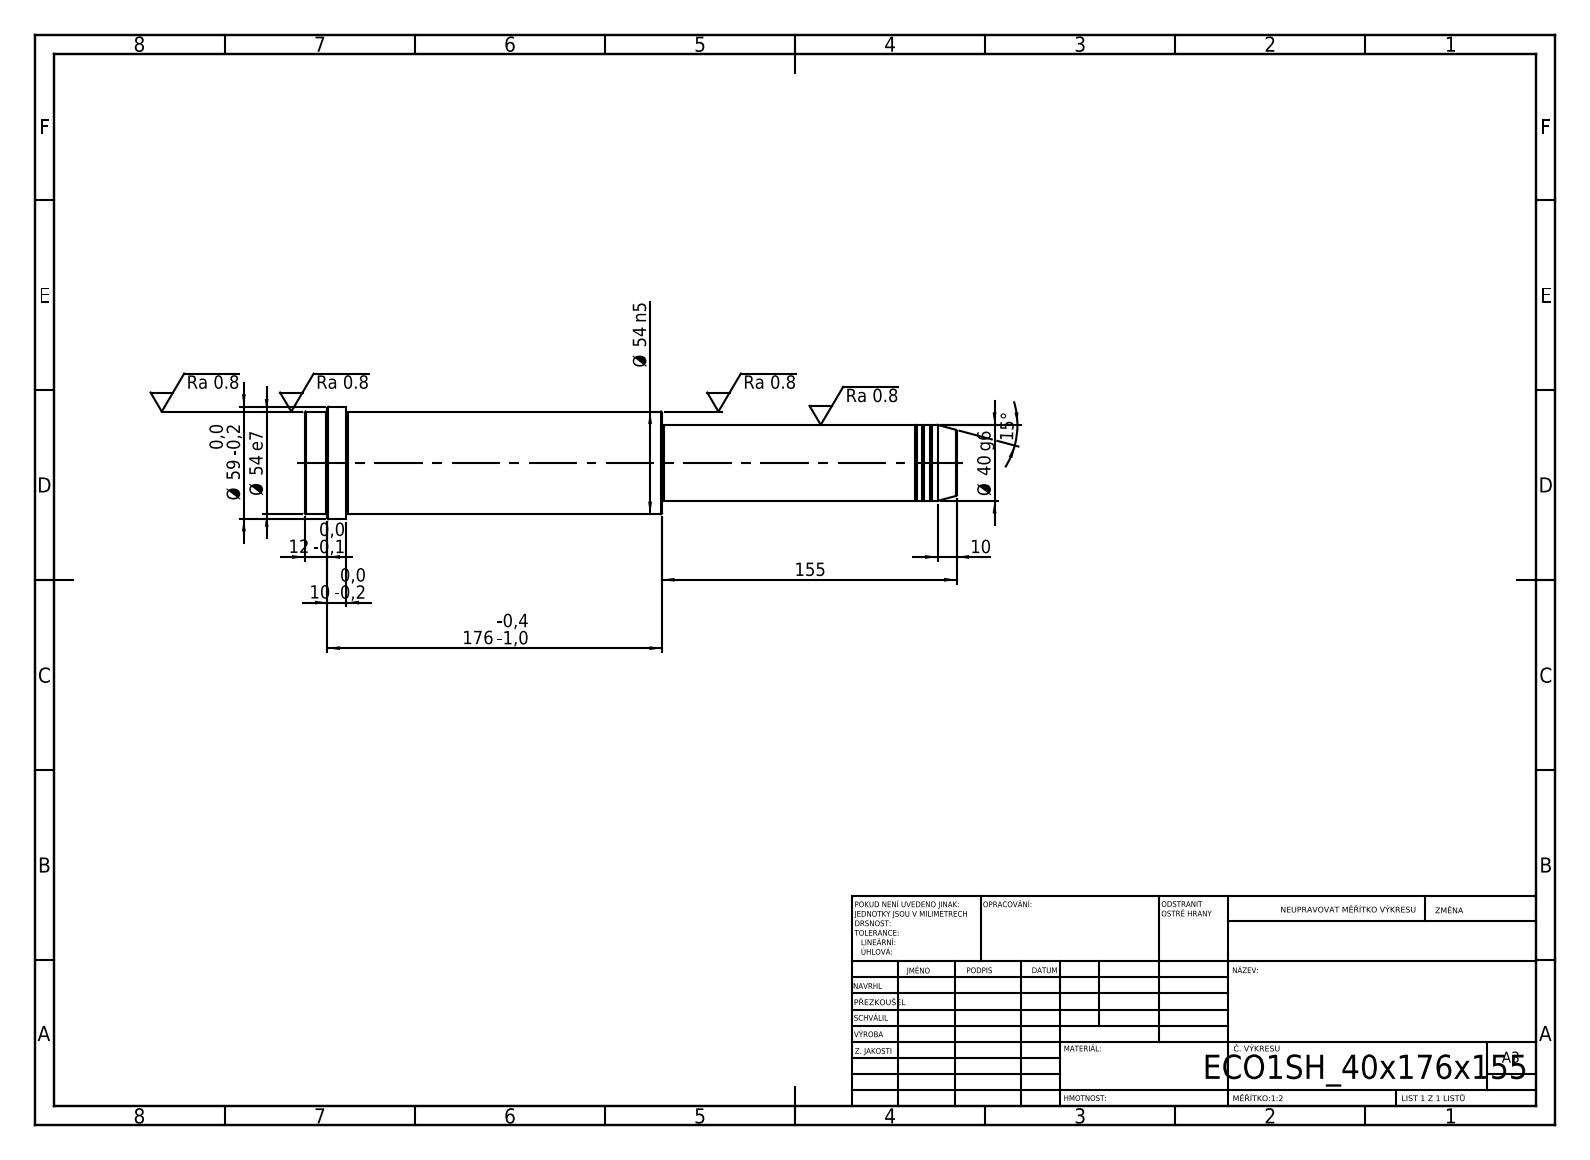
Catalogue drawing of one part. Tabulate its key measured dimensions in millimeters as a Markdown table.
| quantity | value |
| --- | --- |
| STEP written by | SolidWorks 2019 (CONFIG_CONTROL_DESIGN) |
| units | millimeters |
| bodies | 1 solid, 52 faces (6 planar, 16 cylindrical, 30 other) |
| overall size | 343 × 59 × 59 |
| volume | 627 760 mm³ |
| surface area | 56 986 mm² |
| round bosses / shafts (diameter × count) | 59 × 1, 54 × 1, 40 × 1, 39 × 1 |
| main face-to-face distances | 188, 155, 343, 321, 166, 22, 331, 176, 10, 12 |
